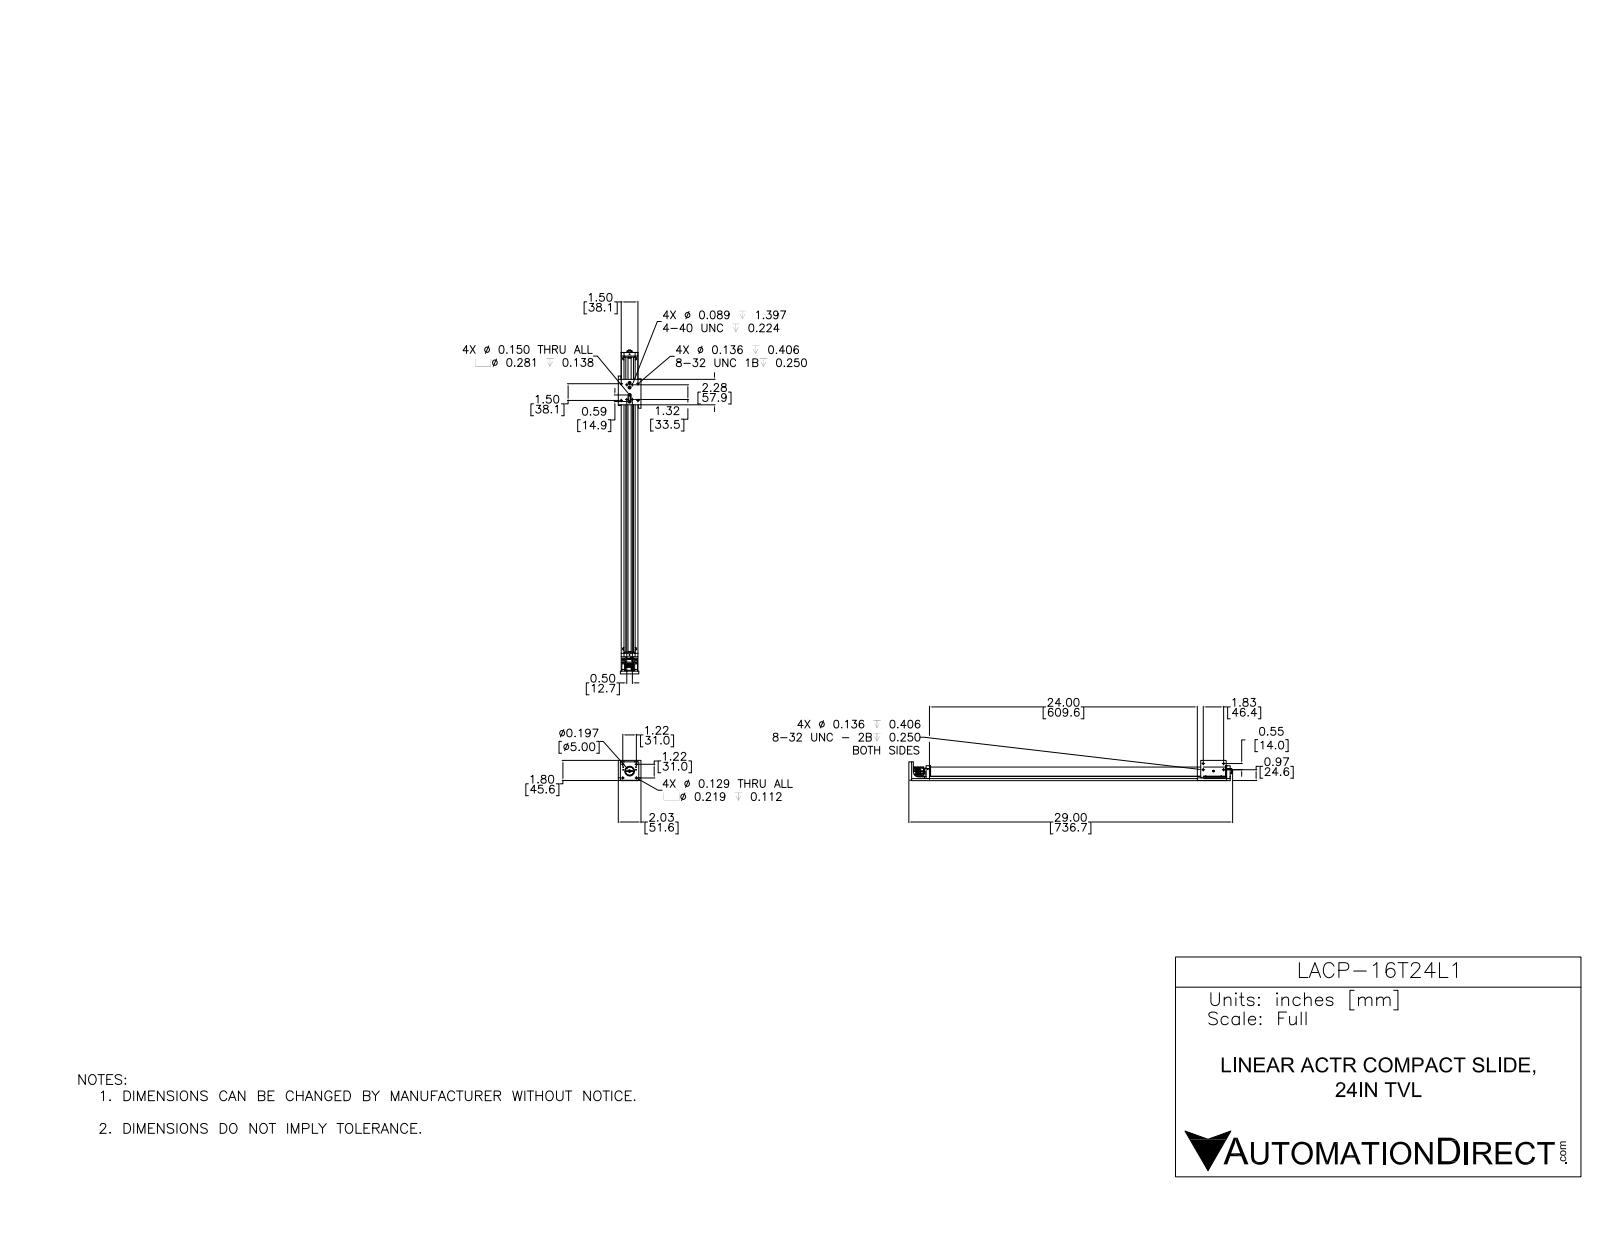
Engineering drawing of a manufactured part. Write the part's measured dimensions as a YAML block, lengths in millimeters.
part_name: "LACP-16T24L1; LACP-16T24L1-RAIL; LACP-16TXXL1-CAR"
step_written_by: "SolidWorks 2016 (AUTOMOTIVE_DESIGN)"
units: millimeters
bodies: {solids: 25, faces: 887, planar: 280, cylindrical: 517, other: 90}
overall_size: [736.5, 51.6, 46]
volume: 518200
surface_area: 226800
round_holes:
  - {diameter: 2.3, count: 16}
  - {diameter: 7.1, count: 16}
  - {diameter: 4.3, count: 14}
  - {diameter: 3.8, count: 9}
  - {diameter: 3.5, count: 8}
  - {diameter: 3.5, count: 7}
  - {diameter: 7.1, count: 7}
  - {diameter: 1.8, count: 4}
  - {diameter: 3.3, count: 4}
  - {diameter: 3.3, count: 4}
  - {diameter: 5.6, count: 4}
  - {diameter: 5, count: 3}
round_bosses_or_shafts:
  - {diameter: 4, count: 3}
  - {diameter: 3.8, count: 2}
  - {diameter: 25.4, count: 1}
  - {diameter: 19, count: 1}
  - {diameter: 18, count: 1}
  - {diameter: 17.1, count: 1}
  - {diameter: 17, count: 1}
  - {diameter: 15, count: 1}
partial_cylinders:
  - {radius: 1.2, count: 4}
  - {radius: 1.6, count: 4}
  - {radius: 2.4, count: 4}
  - {radius: 3.2, count: 3}
  - {radius: 1.3, count: 2}
  - {radius: 1.9, count: 2}
  - {radius: 3.6, count: 2}
  - {radius: 6.4, count: 2}
face_to_face_distances: [4.7, 31, 26.2, 6.7, 44.8, 38.1, 22.2, 29.3, 15.5, 22.6]
hole_center_spacings: [102.4, 203.6, 101.6, 305.1, 203.2, 12.7, 104.7, 304.8]
